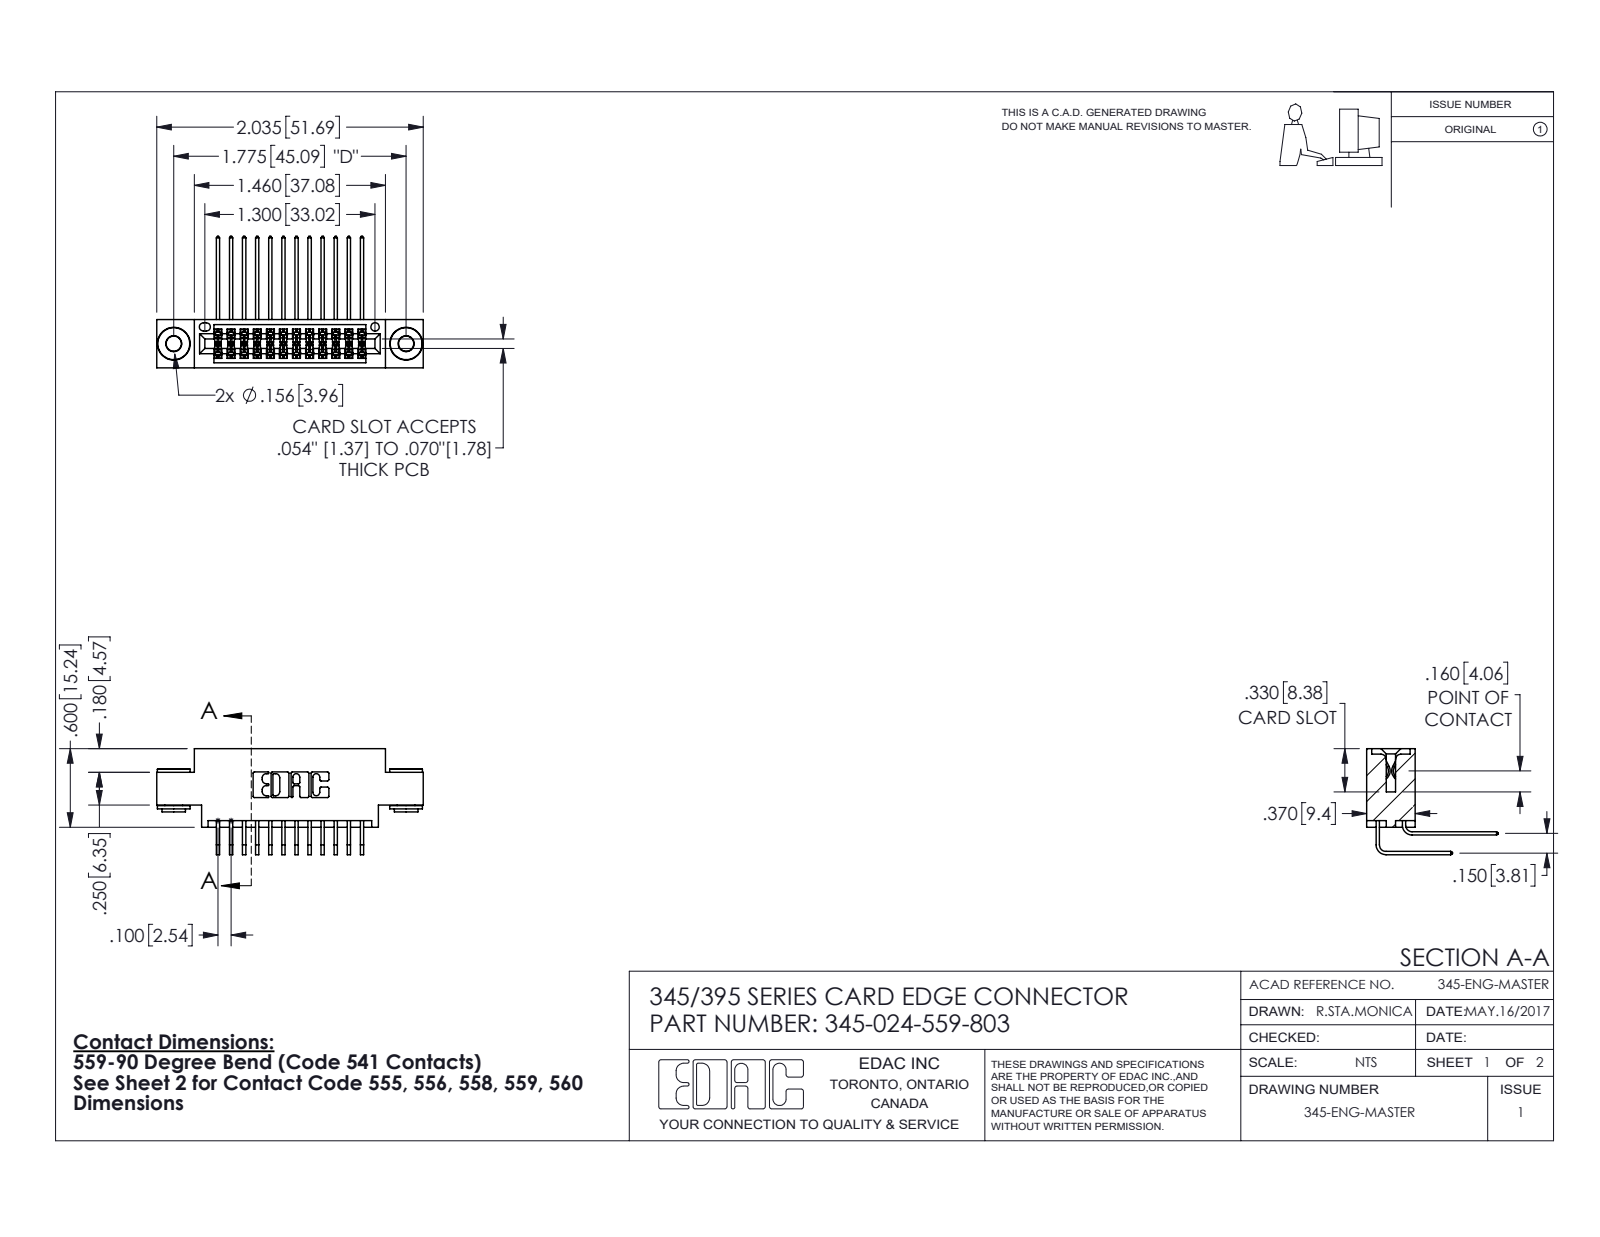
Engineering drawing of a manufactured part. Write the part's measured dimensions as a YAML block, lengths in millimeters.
part_name: "345-250-002_345-250-002-102; 345-292-001_559 Tail - 2; 345-292-001_558 559 Tail - 1; 345 Part_0.170 Offset - 0.156 Dia-TH (+1 more)"
step_written_by: "SolidWorks 2016 (CONFIG_CONTROL_DESIGN)"
units: millimeters
bodies: {solids: 27, faces: 1416, planar: 934, cylindrical: 474, other: 8}
overall_size: [51.7, 25.5, 20.5]
volume: 4790
surface_area: 7497
round_holes:
  - {diameter: 2.9, count: 2}
  - {diameter: 4, count: 2}
  - {diameter: 1.6, count: 1}
round_bosses_or_shafts:
  - {diameter: 6.4, count: 2}
  - {diameter: 4.6, count: 2}
  - {diameter: 3.5, count: 2}
partial_cylinders:
  - {radius: 0.2, count: 47}
  - {radius: 0.3, count: 22}
  - {radius: 0.2, count: 6}
  - {radius: 0.8, count: 6}
  - {radius: 0.7, count: 3}
  - {radius: 0.4, count: 2}
  - {radius: 0.5, count: 2}
  - {radius: 0.6, count: 2}
face_to_face_distances: [1.8, 7.6, 9.4, 5.1, 2.5, 6.9, 0.6, 4.4, 3.8, 5.7]
hole_center_spacings: [6.9, 39.2, 45.1]
